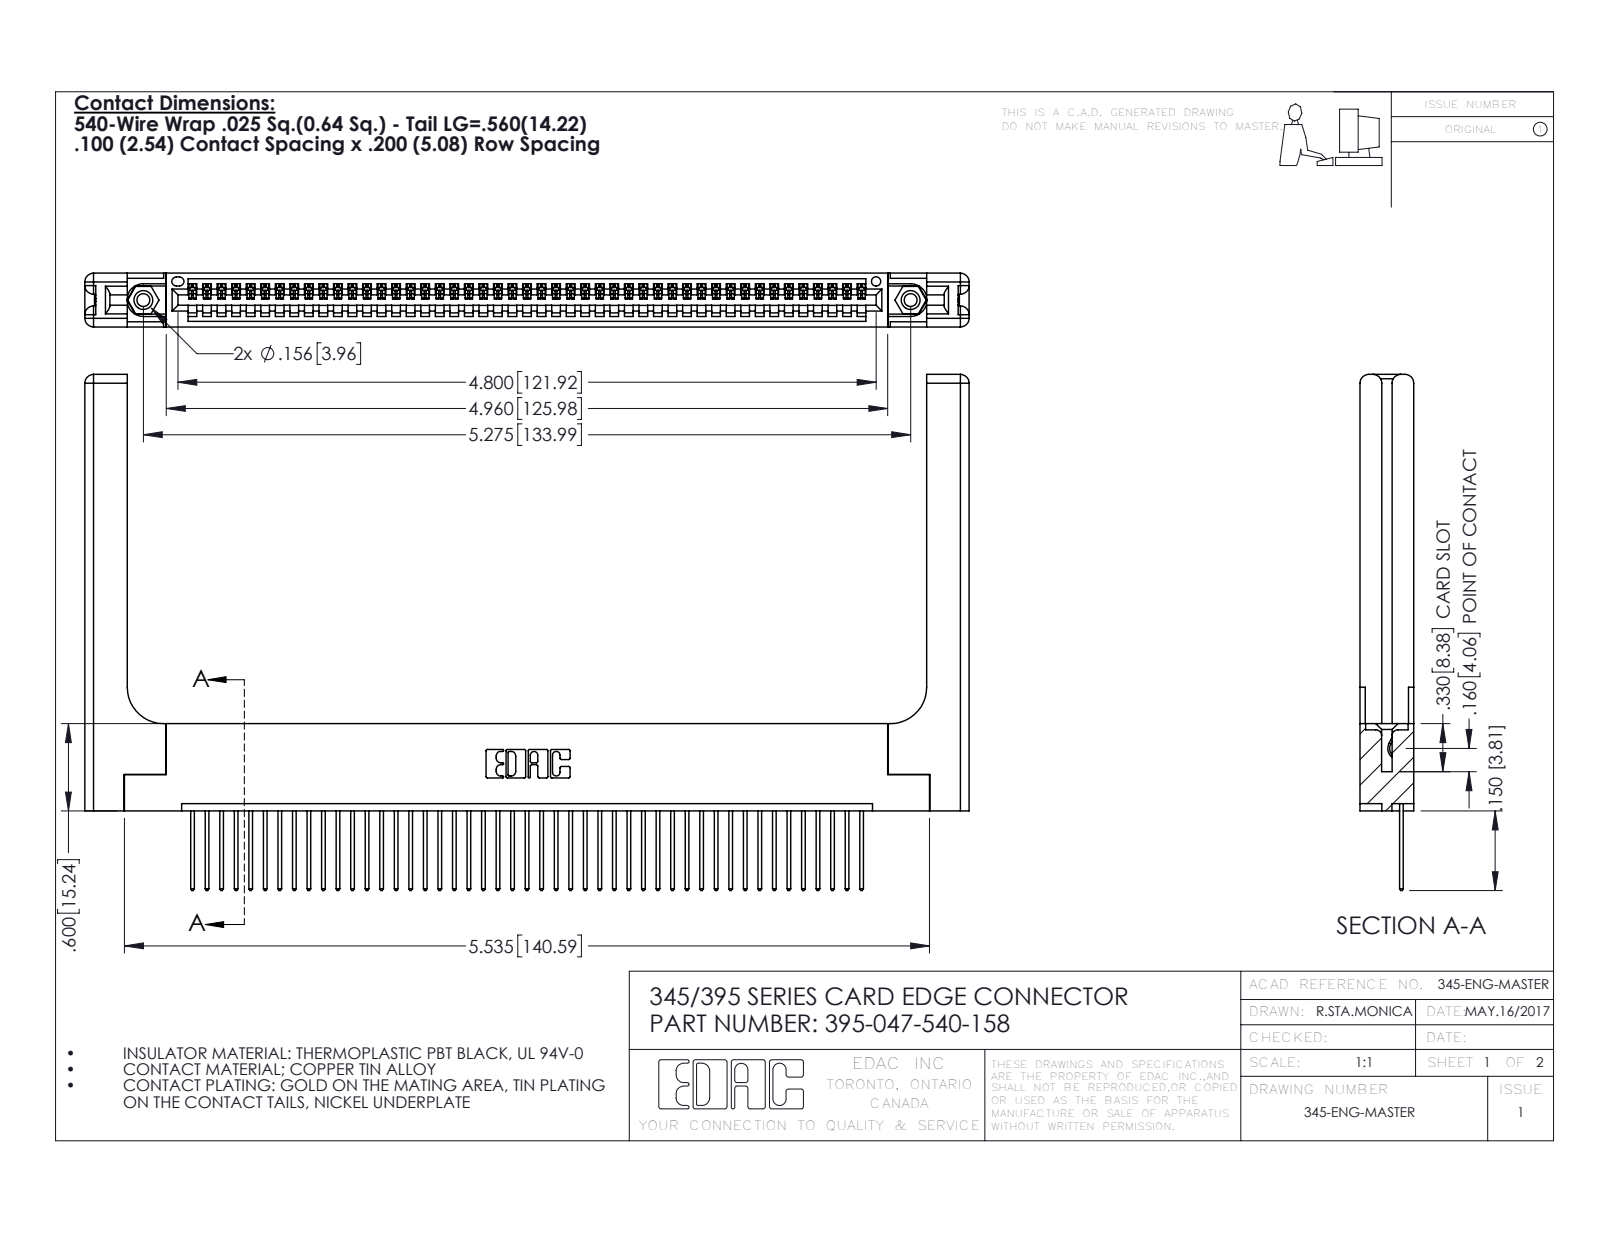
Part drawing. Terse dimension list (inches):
name: 345-250-001_345-250-001-102; 345-292-001_345-293-140; 395-047-540-158; 345-220-058_345-220-058 (+1 more)
written by: SolidWorks 2016 (CONFIG_CONTROL_DESIGN)
unit: in
bodies: 52 solids, 3108 faces (2108 planar, 940 cylindrical, 60 other)
size: 6.079 × 3.547 × 0.37
volume: 1.42 in³; area: 39.46 in²
holes: 2× ⌀0.089, 2× ⌀0.125, 2× ⌀0.156, 1× ⌀0.064
bosses: 2× ⌀0.155
rounds: 94× R0.006, 94× R0.01, 22× R0.01, 16× R0.06, 6× R0.007, 6× R0.031, 3× R0.026, 2× R0.03
face distances: 0.072, 0.37, 0.298, 0.098, 0.272, 0.025, 0.2, 0.225, 0.148, 0.15
hole spacings: 0.27, 5.039, 5.275
